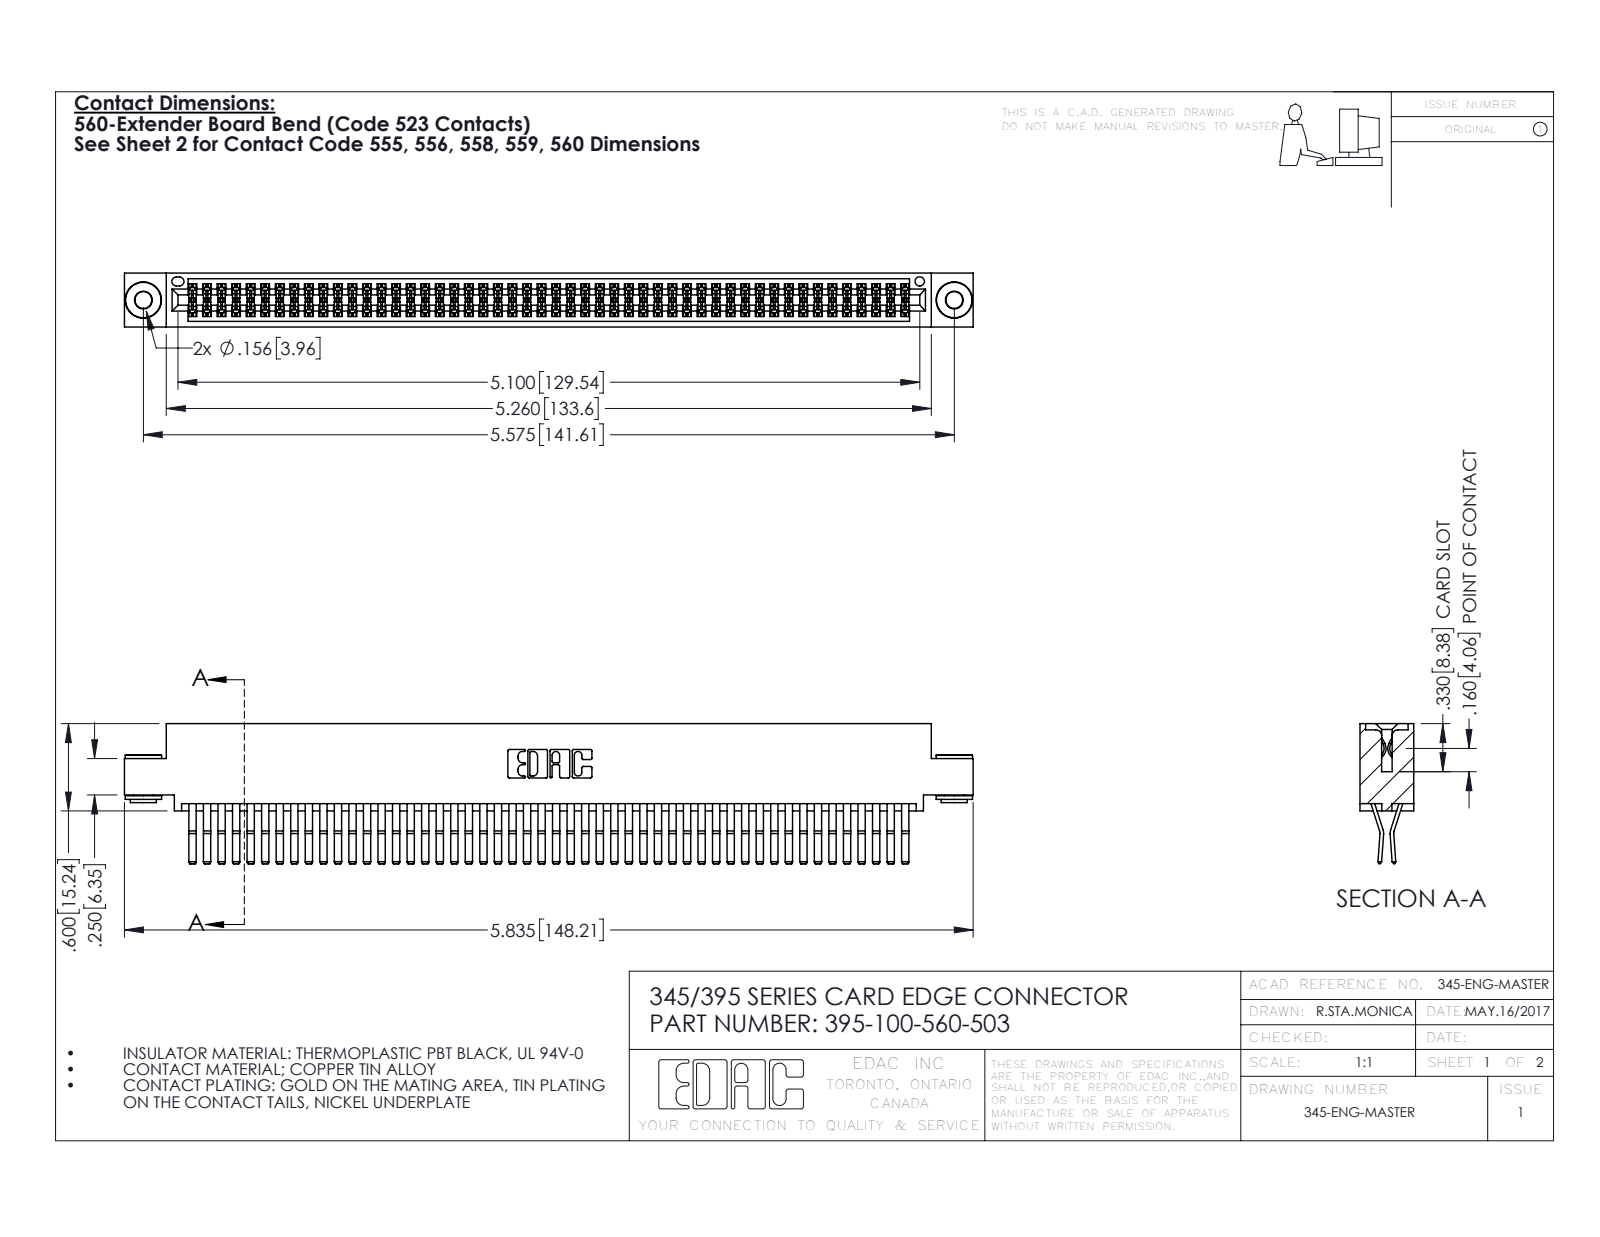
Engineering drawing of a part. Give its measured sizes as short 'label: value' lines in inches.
name: 345-250-002_345-250-002-102; 345-292-001_560 Tail; 345 Part_0.110 Offset - 0.156 Dia-TH; 395-100-560-503
written by: SolidWorks 2016 (CONFIG_CONTROL_DESIGN)
unit: in
bodies: 103 solids, 5368 faces (3394 planar, 1966 cylindrical, 8 other)
size: 5.835 × 0.962 × 0.37
volume: 0.92 in³; area: 37.85 in²
holes: 2× ⌀0.116, 2× ⌀0.156, 1× ⌀0.064
bosses: 2× ⌀0.25, 2× ⌀0.18, 2× ⌀0.136
rounds: 151× R0.006, 22× R0.01, 6× R0.007, 6× R0.031, 3× R0.026, 2× R0.01, 2× R0.014, 2× R0.019
face distances: 0.025, 0.072, 0.298, 0.37, 0.2, 0.098, 0.272, 0.225, 0.175, 0.149
hole spacings: 0.27, 5.339, 5.575
